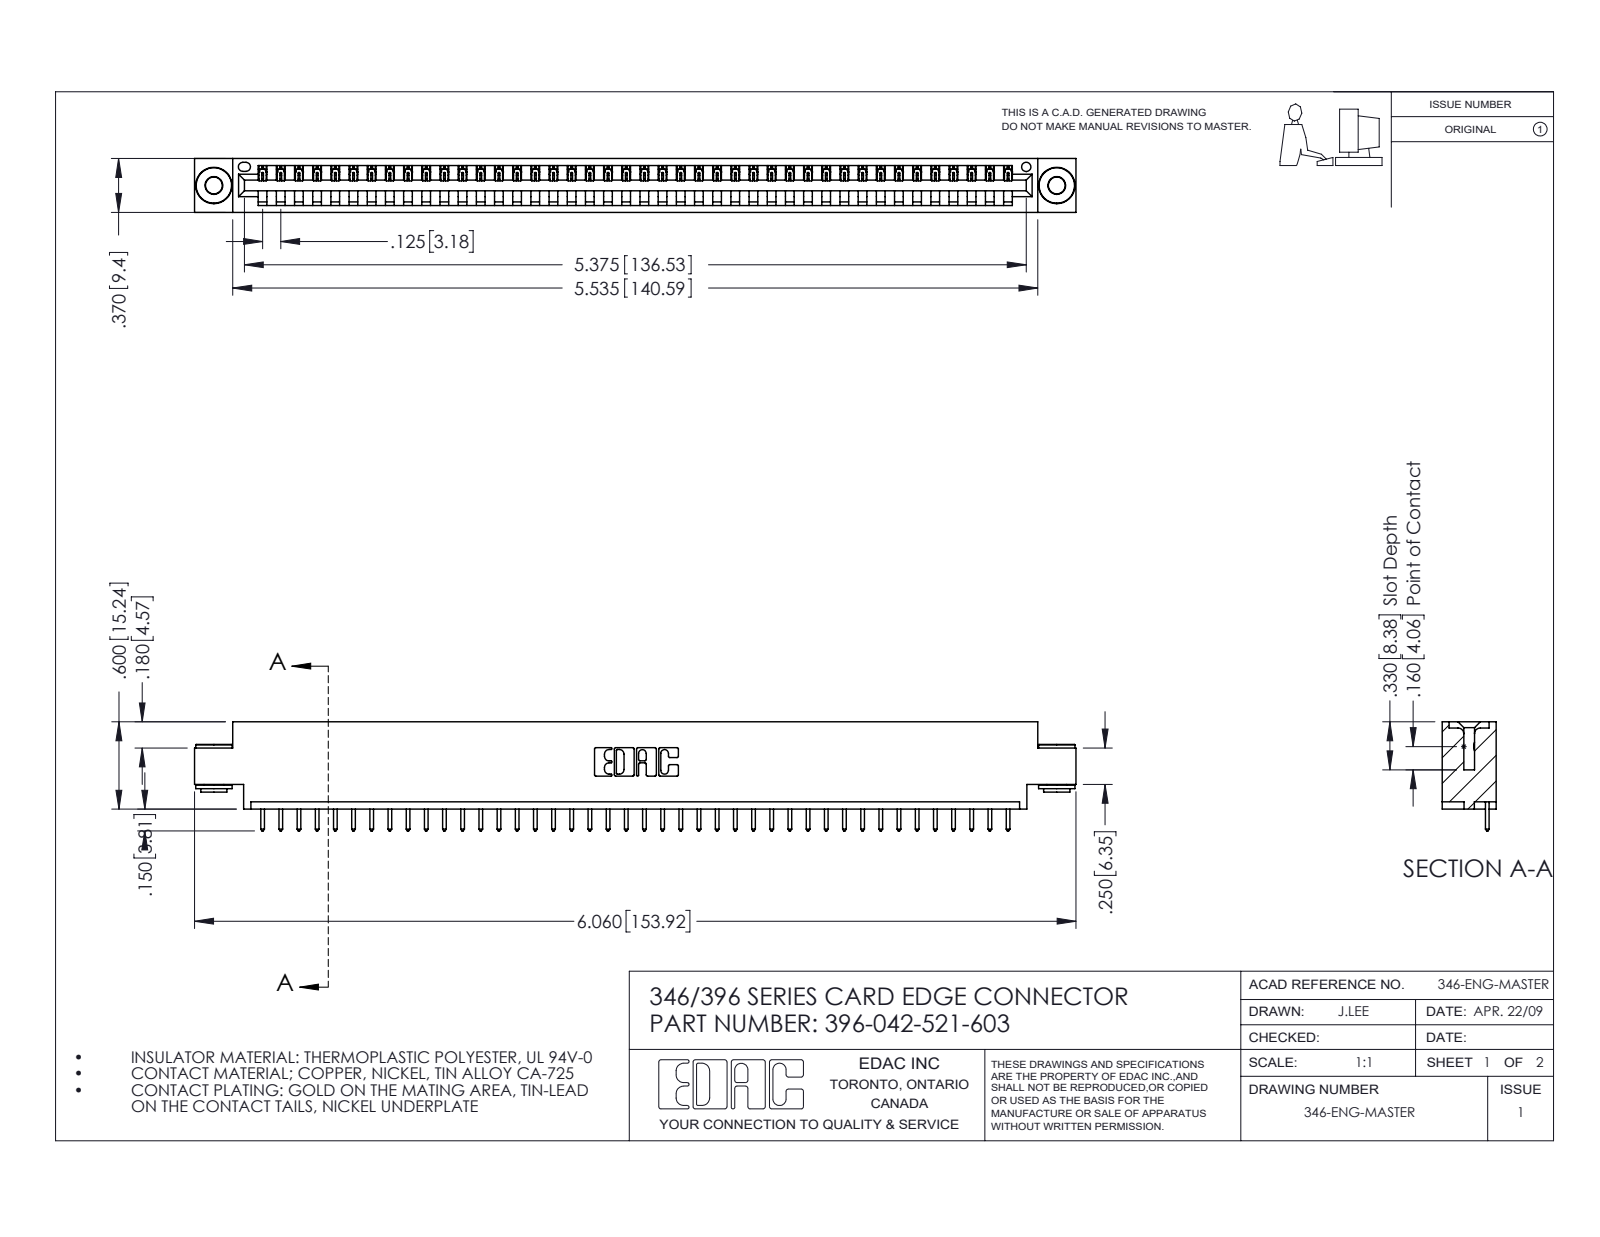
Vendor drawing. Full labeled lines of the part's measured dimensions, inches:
Part name (STEP PRODUCT): 396-042-521-603; 345-250-002_345-250-002-102; 345-292-001_345-293-121; 346 Part_0.170 Offset - 0.156 Dia-TH
STEP written by: SolidWorks 2016 (CONFIG_CONTROL_DESIGN)
Units: inches
Bodies: 45 solids, 2600 faces (1770 planar, 822 cylindrical, 8 other)
Overall size (bounding box): 6.06 × 0.75 × 0.37
Volume: 0.884 in³ · Surface area: 27.9 in²
Round holes (diameter × count): ⌀0.116 ×2, ⌀0.156 ×2, ⌀0.064 ×1
Round bosses / shafts (diameter × count): ⌀0.25 ×2, ⌀0.18 ×2, ⌀0.136 ×2
Partial cylindrical surfaces — rounded edges, fillets, slot ends (radius × count): R0.006 ×84, R0.01 ×84, R0.01 ×22, R0.007 ×6, R0.031 ×6, R0.026 ×3, R0.031 ×2, R0.04 ×2
Main face-to-face distances: 0.048, 0.322, 0.37, 0.25, 0.025, 0.072, 0.298, 0.148, 0.222, 0.1
Hole centre spacings: 0.246, 5.586, 5.795
